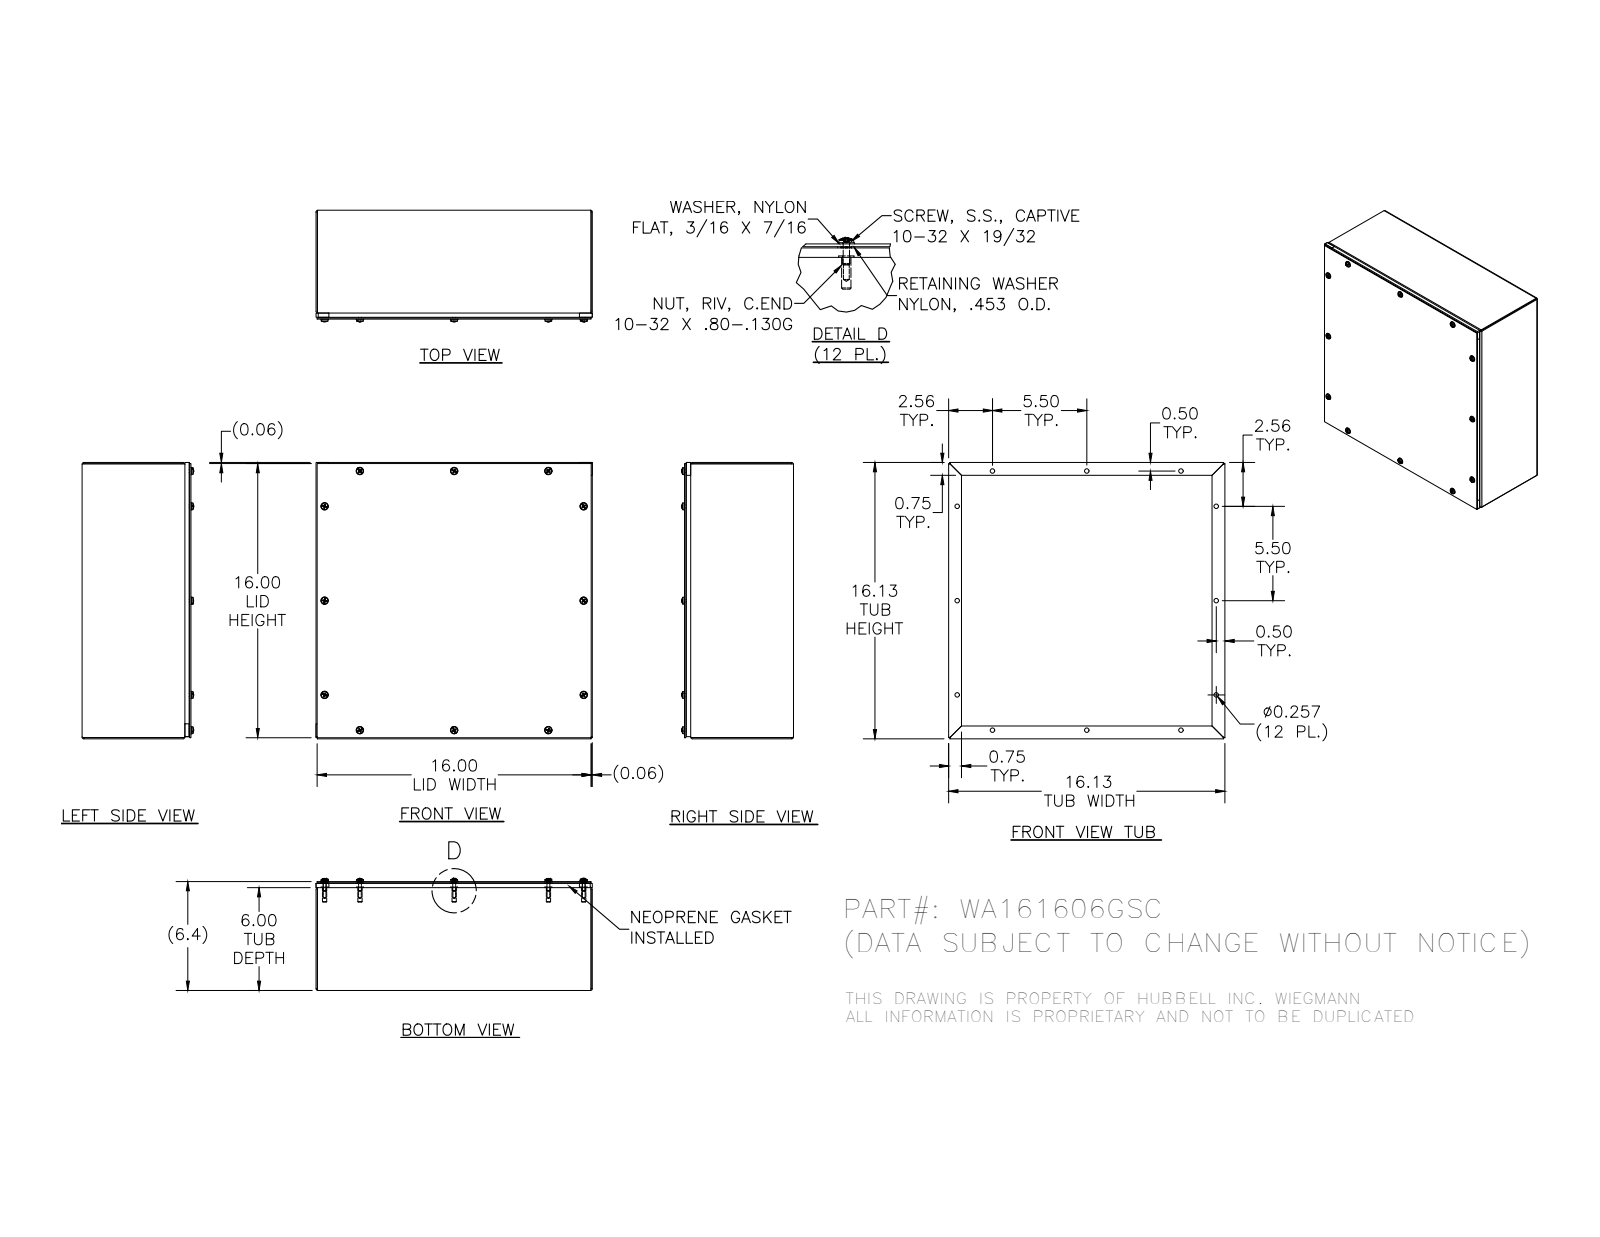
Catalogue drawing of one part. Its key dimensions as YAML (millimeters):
part_name: "39077; 37210; WA161606GSCBKP; WA161606GSC (+3 more)"
step_written_by: "SolidWorks 2014 (AUTOMOTIVE_DESIGN)"
units: millimeters
bodies: {solids: 53, faces: 1258, planar: 590, cylindrical: 328, other: 340}
overall_size: [409.6, 409.6, 165.4]
volume: 1289000
surface_area: 1294000
round_holes:
  - {diameter: 4.8, count: 12}
  - {diameter: 6.5, count: 12}
  - {diameter: 7.1, count: 12}
  - {diameter: 7.1, count: 12}
  - {diameter: 4, count: 11}
  - {diameter: 5, count: 11}
round_bosses_or_shafts:
  - {diameter: 11.5, count: 12}
  - {diameter: 11.1, count: 12}
  - {diameter: 4.2, count: 12}
  - {diameter: 10.3, count: 11}
  - {diameter: 6.3, count: 11}
partial_cylinders:
  - {radius: 2.3, count: 12}
  - {radius: 0.8, count: 8}
  - {radius: 2.7, count: 8}
face_to_face_distances: [1.9, 159.6, 407.7, 161.4, 157.7, 409.6, 405.8, 9, 150.5, 7.2]
hole_center_spacings: [139.7, 383.4, 335.9, 199.1, 279.4, 383.4, 199.1, 408.8]
